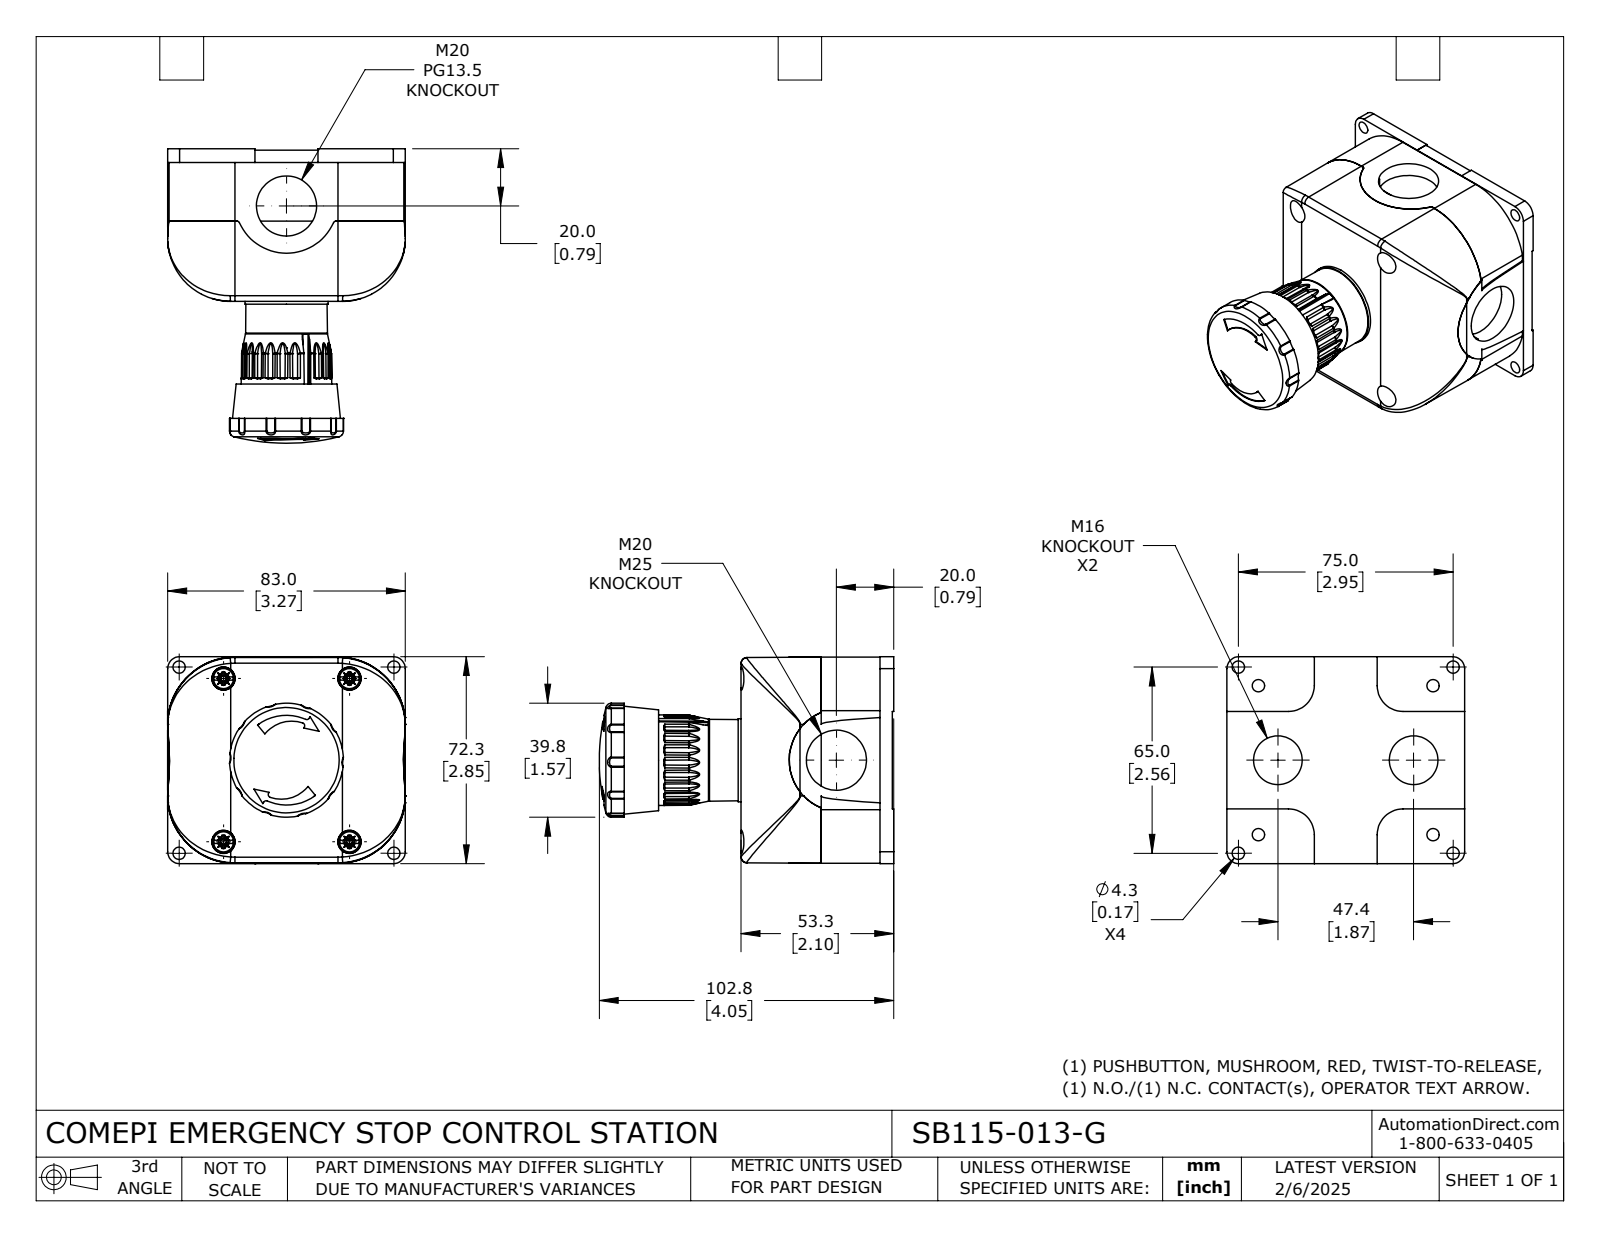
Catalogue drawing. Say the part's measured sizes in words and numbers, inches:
The part is named "SB115-013-G". Its 3-D file was written by "SolidWorks 2024 (CONFIG_CONTROL_DESIGN)". It is 5 solids with 901 faces: 353 planar, 192 cylindrical and 356 other. Overall it measures 4.048 by 3.268 by 2.846 inches. Its volume is 14.31 cubic inches and its surface area 106.3 square inches. Round holes: 8 of diameter 0.169, 4 of diameter 0.323, 2 of diameter 0.669, 2 of diameter 0.827, 1 of diameter 0.051, 1 of diameter 0.713, 1 of diameter 0.854. Round bosses or shafts: 4 of diameter 0.276, 1 of diameter 1.142, 1 of diameter 0.925, 1 of diameter 0.874, 1 of diameter 0.843. Partial cylindrical surfaces (rounded edges, fillets, slot ends): 28 of radius 0.039, 10 of radius 0.268, 4 of radius 0.035, 4 of radius 0.079, 4 of radius 0.354, 4 of radius 0.38, 4 of radius 0.925, 2 of radius 0.01. The main face-to-face distances are 0.976, 0.098, 0.878, 2.079, 1.98, 1.102, 0.118, 0.02, 0.996, 2.098. The hole center spacings are 0.376, 1.058, 1.39, 1.578, 1.954, 2.32, 2.367, 2.689.
